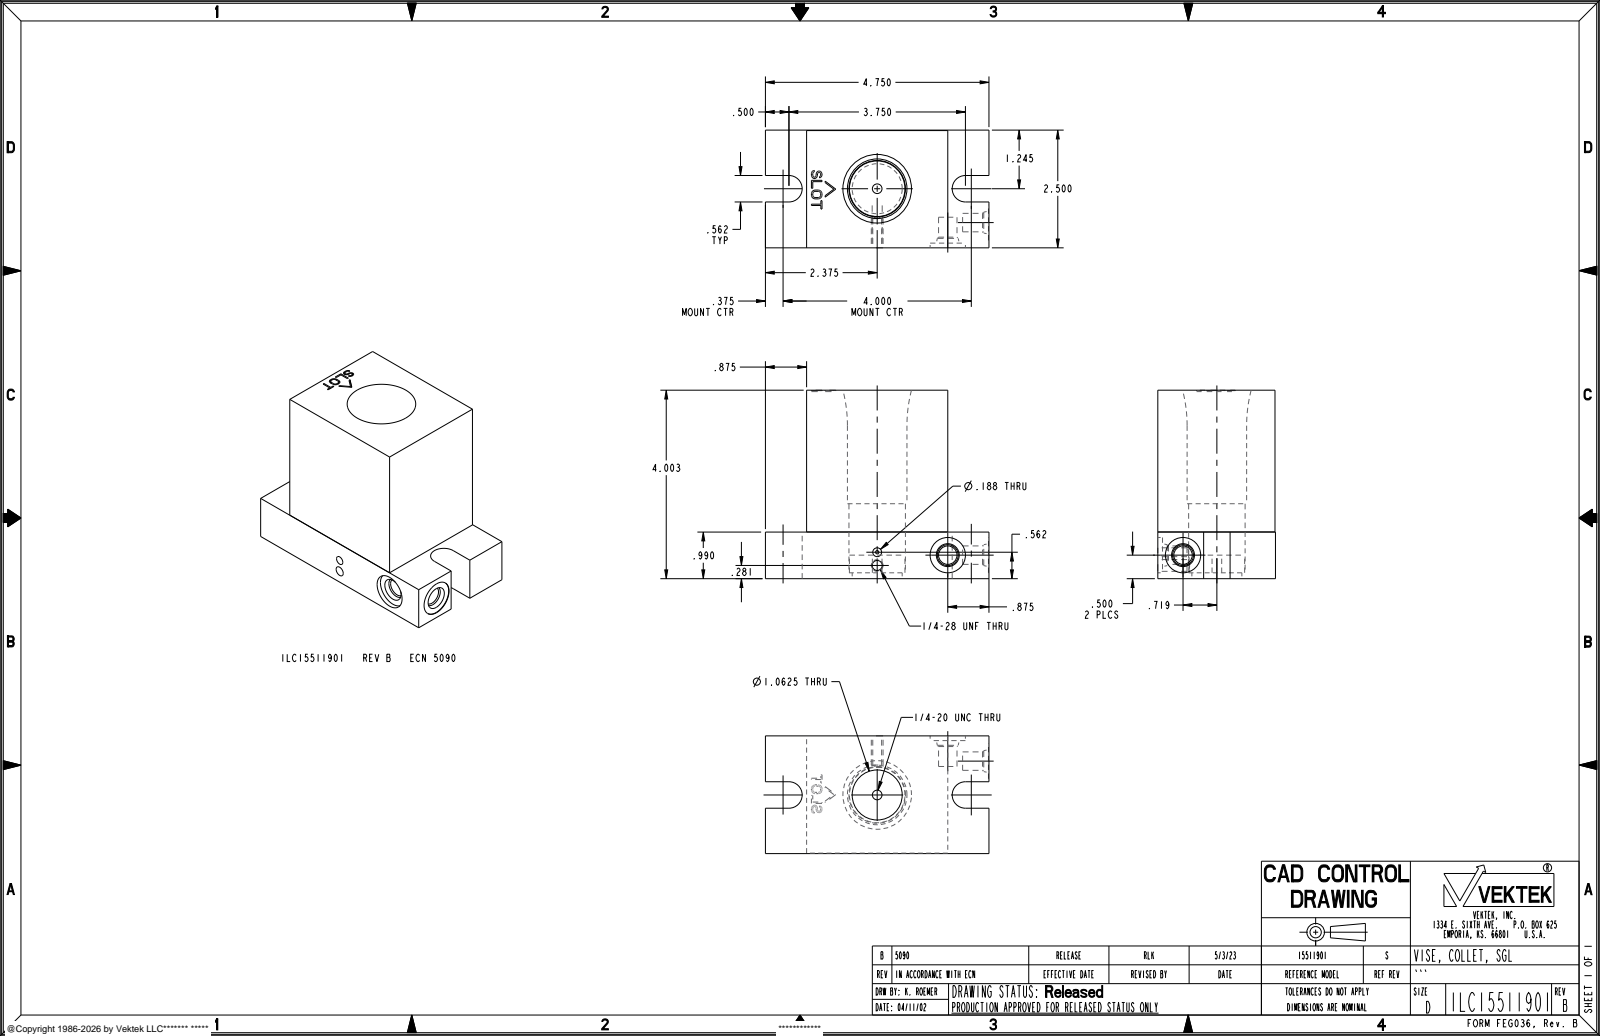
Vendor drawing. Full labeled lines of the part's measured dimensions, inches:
Part name (STEP PRODUCT): ILC15511901
STEP written by: CREO PARAMETRIC BY PTC INC, 2021164 (AUTOMOTIVE_DESIGN)
Units: inches
Bodies: 2 solids, 194 faces (152 planar, 30 cylindrical, 12 other)
Overall size (bounding box): 4.75 × 4.003 × 2.5
Volume: 28.7 in³ · Surface area: 104.8 in²
Round holes (diameter × count): ⌀0.392 ×2, ⌀0.75 ×2, ⌀0.188 ×1, ⌀0.205 ×1, ⌀0.213 ×1, ⌀0.25 ×1, ⌀1.063 ×1, ⌀1.2 ×1, ⌀1.265 ×1
Round bosses / shafts (diameter × count): ⌀1.18 ×1
Partial cylindrical surfaces — rounded edges, fillets, slot ends (radius × count): R0.281 ×2
Main face-to-face distances: 0.99, 2.49, 3, 0.993, 4.003, 3.013, 3.01, 2.5, 0.875, 3.875
Hole centre spacings: 0.281, 1.501, 1.516
